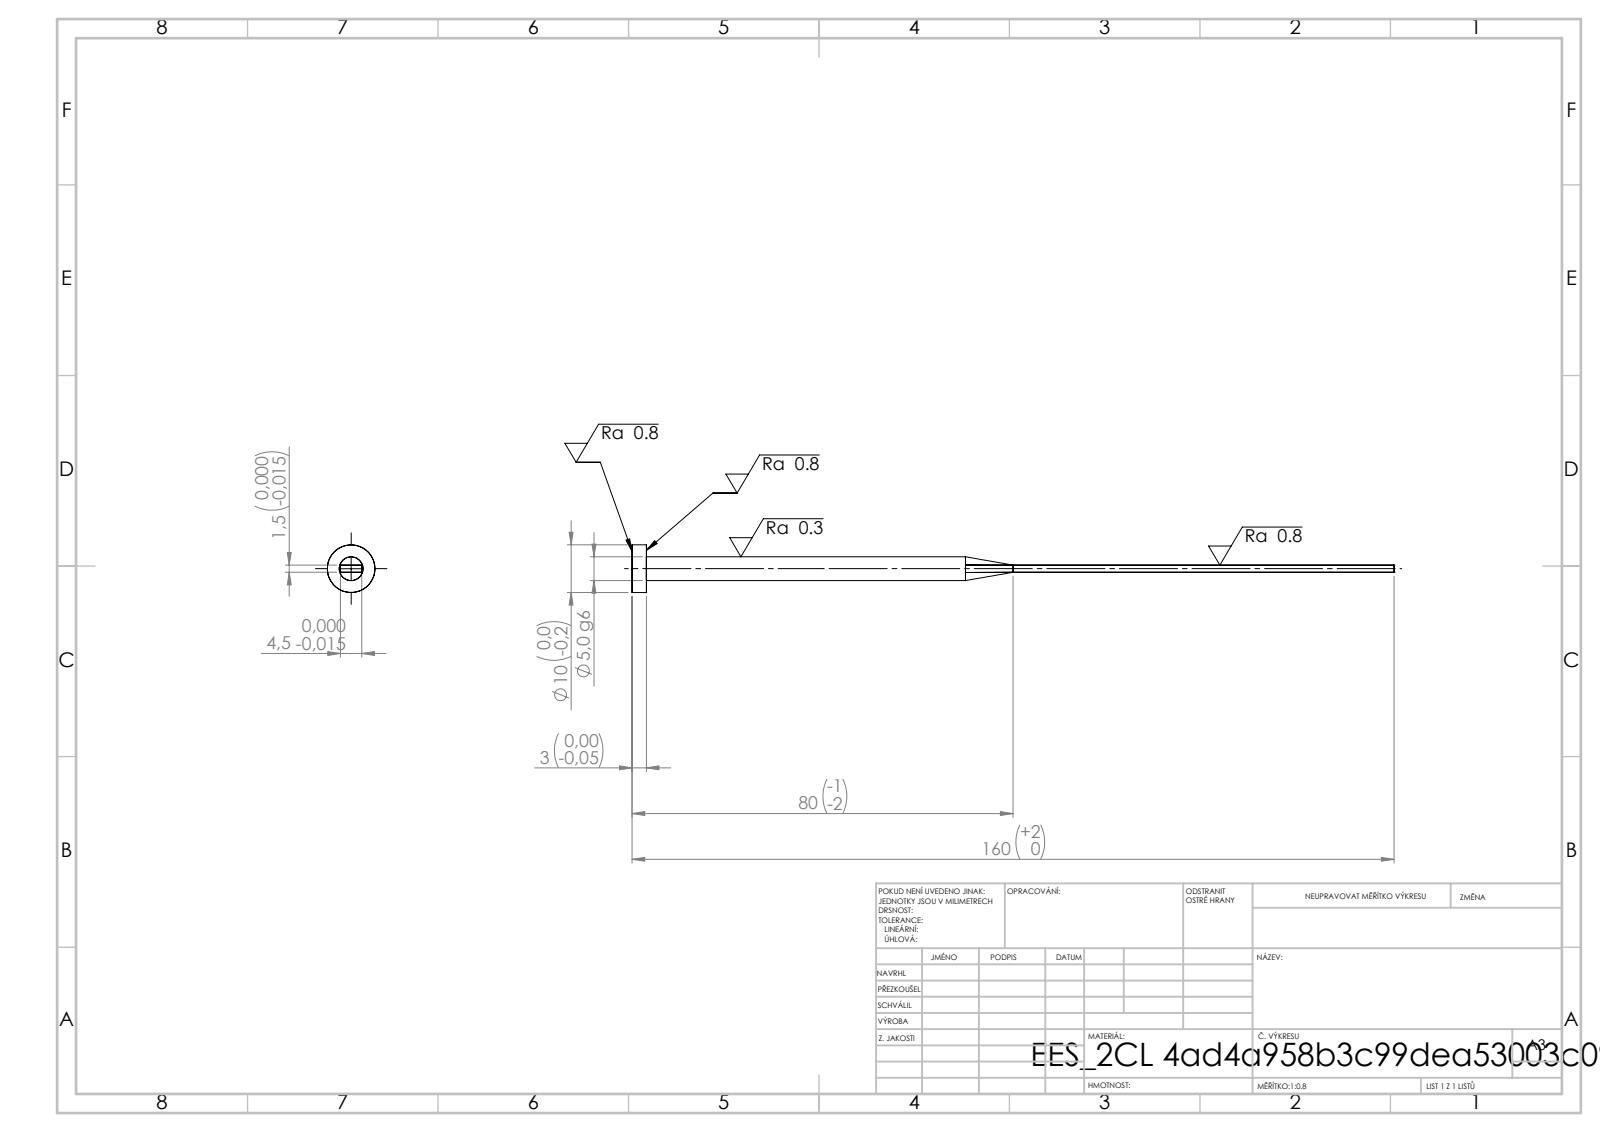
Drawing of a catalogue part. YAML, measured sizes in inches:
step_written_by: "SolidWorks 2019 (CONFIG_CONTROL_DESIGN)"
units: inches
bodies: {solids: 1, faces: 15, planar: 7, cylindrical: 4, other: 4}
overall_size: [6.299, 0.394, 0.394]
volume: 0.135
surface_area: 3.698
round_bosses_or_shafts:
  - {diameter: 0.394, count: 1}
  - {diameter: 0.197, count: 1}
face_to_face_distances: [0.059, 0.177, 0.118, 6.299, 6.181]
